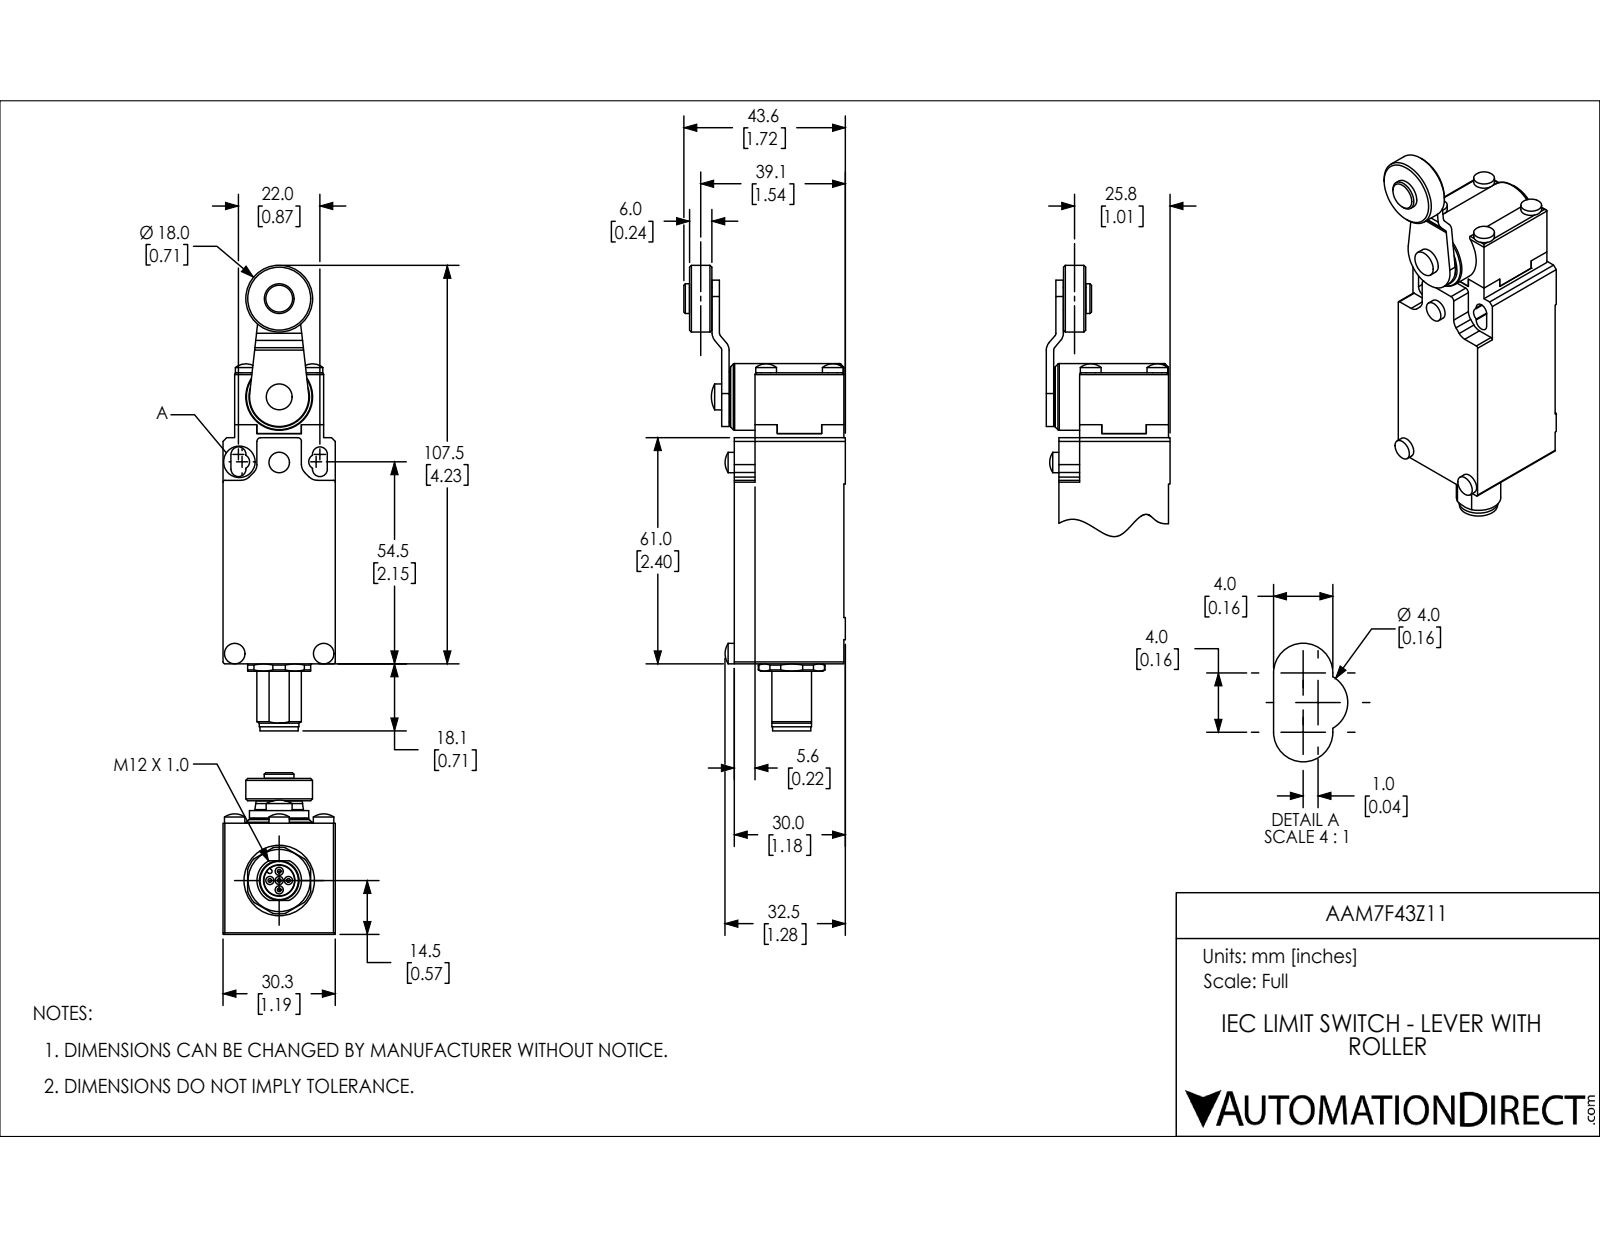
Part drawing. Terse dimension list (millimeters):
name: AAM7F43Z11
written by: SolidWorks 2018 (AUTOMOTIVE_DESIGN)
unit: mm
bodies: 4 solids, 327 faces (130 planar, 141 cylindrical, 56 other)
size: 125.6 × 43.6 × 30.3
volume: 69 840 mm³; area: 18 460 mm²
holes: 5× ⌀2.2, 1× ⌀13, 1× ⌀14, 1× ⌀16
bosses: 5× ⌀1.4, 5× ⌀1, 4× ⌀5.6, 3× ⌀5.5, 2× ⌀18, 1× ⌀14.9, 1× ⌀13.5, 1× ⌀10.7
rounds: 8× R0.5, 6× R2, 6× R3, 4× R1, 1× R0.6, 1× R5, 1× R6, 1× R8
face distances: 30.3, 29.6, 3.1, 27.2, 24, 6, 7, 2, 30, 0.4
hole spacings: 2.5, 3.5, 5
